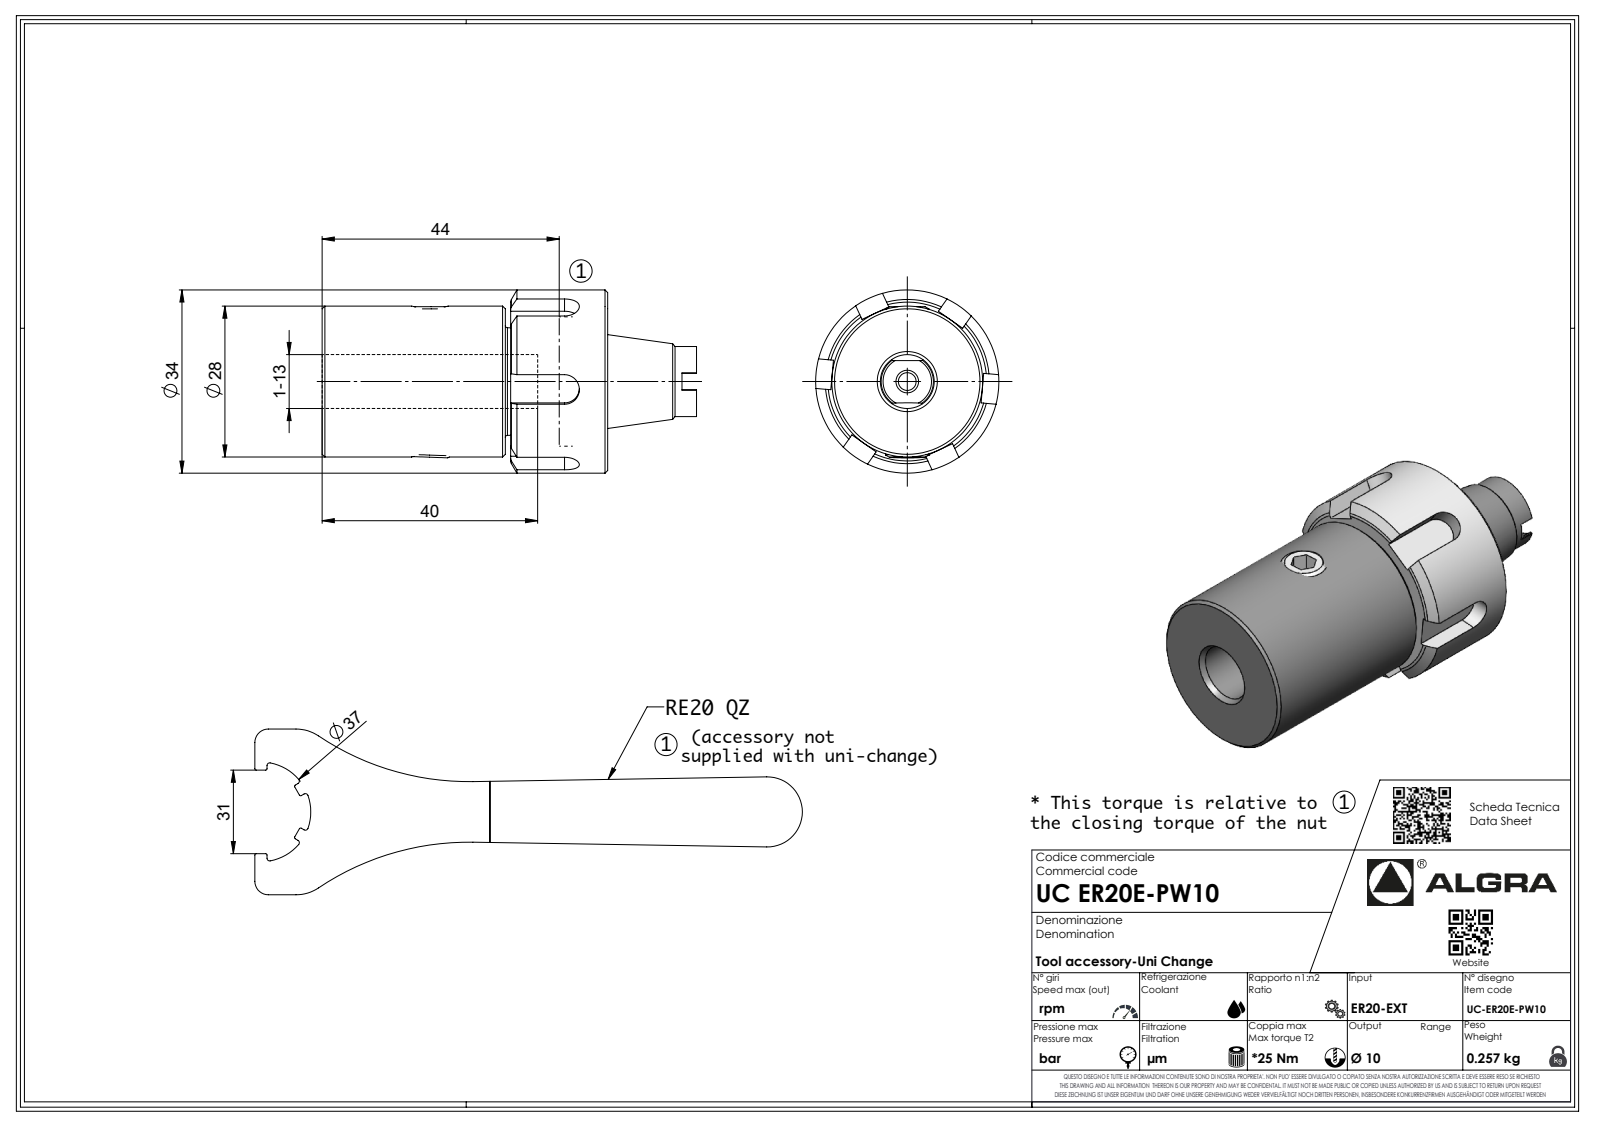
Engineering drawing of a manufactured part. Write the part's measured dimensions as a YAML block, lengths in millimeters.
part_name: "UCER20E-PW10"
step_written_by: "SolidWorks 2016 (AUTOMOTIVE_DESIGN)"
units: millimeters
bodies: {solids: 1, faces: 337, planar: 220, cylindrical: 40, other: 77}
overall_size: [69.5, 34, 34]
volume: 39248
surface_area: 8344
round_holes:
  - {diameter: 1.57, count: 1}
round_bosses_or_shafts:
  - {diameter: 34, count: 1}
  - {diameter: 28, count: 1}
  - {diameter: 19.95, count: 1}
  - {diameter: 13, count: 1}
  - {diameter: 4.77, count: 1}
  - {diameter: 1.27, count: 1}
partial_cylinders:
  - {radius: 0.25, count: 7}
  - {radius: 0.39, count: 7}
  - {radius: 2.78, count: 7}
  - {radius: 2.75, count: 5}
  - {radius: 4, count: 2}
  - {radius: 0.16, count: 1}
face_to_face_distances: [53, 18, 35, 1, 19, 34, 28, 5.5, 16.5, 34.5]
